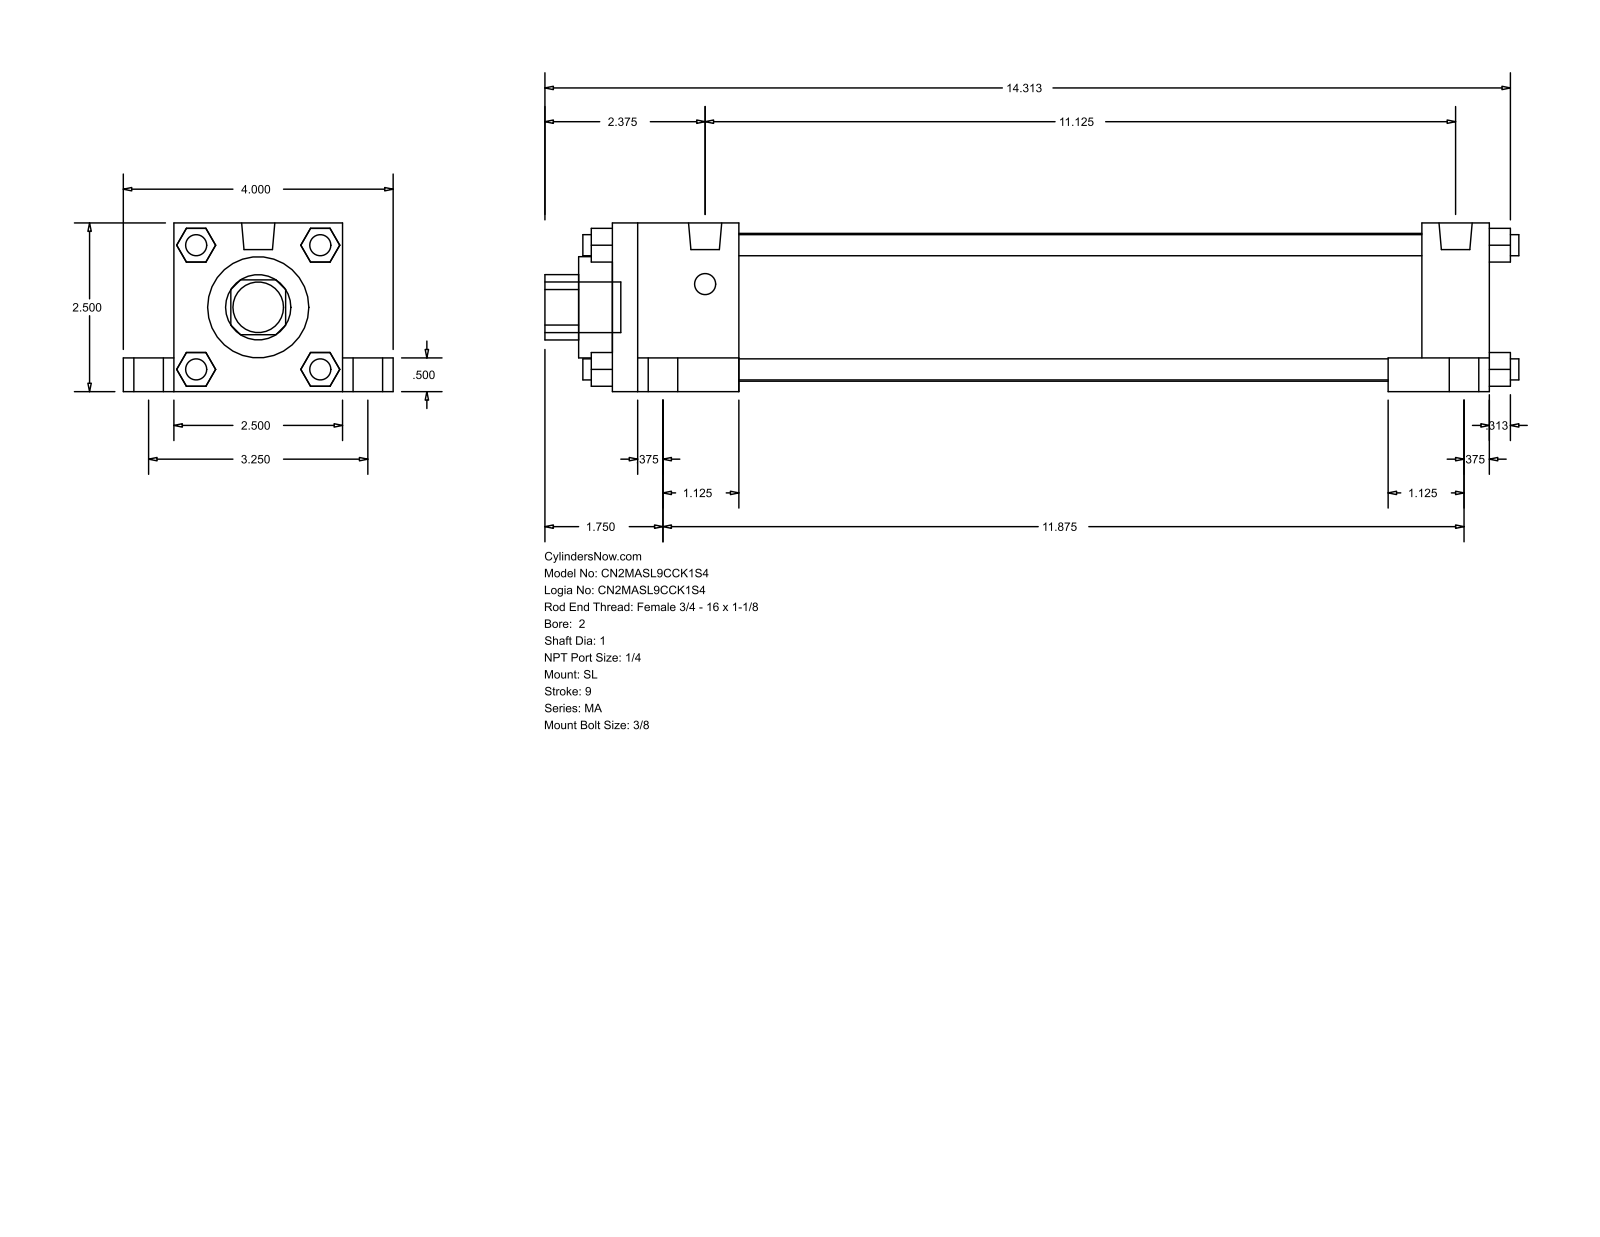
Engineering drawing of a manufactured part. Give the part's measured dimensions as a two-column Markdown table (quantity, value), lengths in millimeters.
| quantity | value |
| --- | --- |
| part name | MA_SL__0200_1 |
| STEP written by | GSSL Pune (CONFIG_CONTROL_DESIGN) |
| units | millimeters |
| bodies | 0 solids, 148 faces (112 planar, 36 cylindrical, 0 other) |
| overall size | 366.71 × 101.6 × 63.5 |
| round holes (diameter × count) | 25.4 × 1, 38.1 × 1, 55.63 × 1 |
| round bosses / shafts (diameter × count) | 7.94 × 8, 17.46 × 4, 11.11 × 4, 12.49 × 2, 19.05 × 1 |
| partial cylindrical surfaces (radius × count) | 12.29 × 1 |
| main face-to-face distances | 63.5, 12.7, 330.2, 19.05, 82.55, 25.4, 50.8, 47.63, 282.57, 304.8 |
